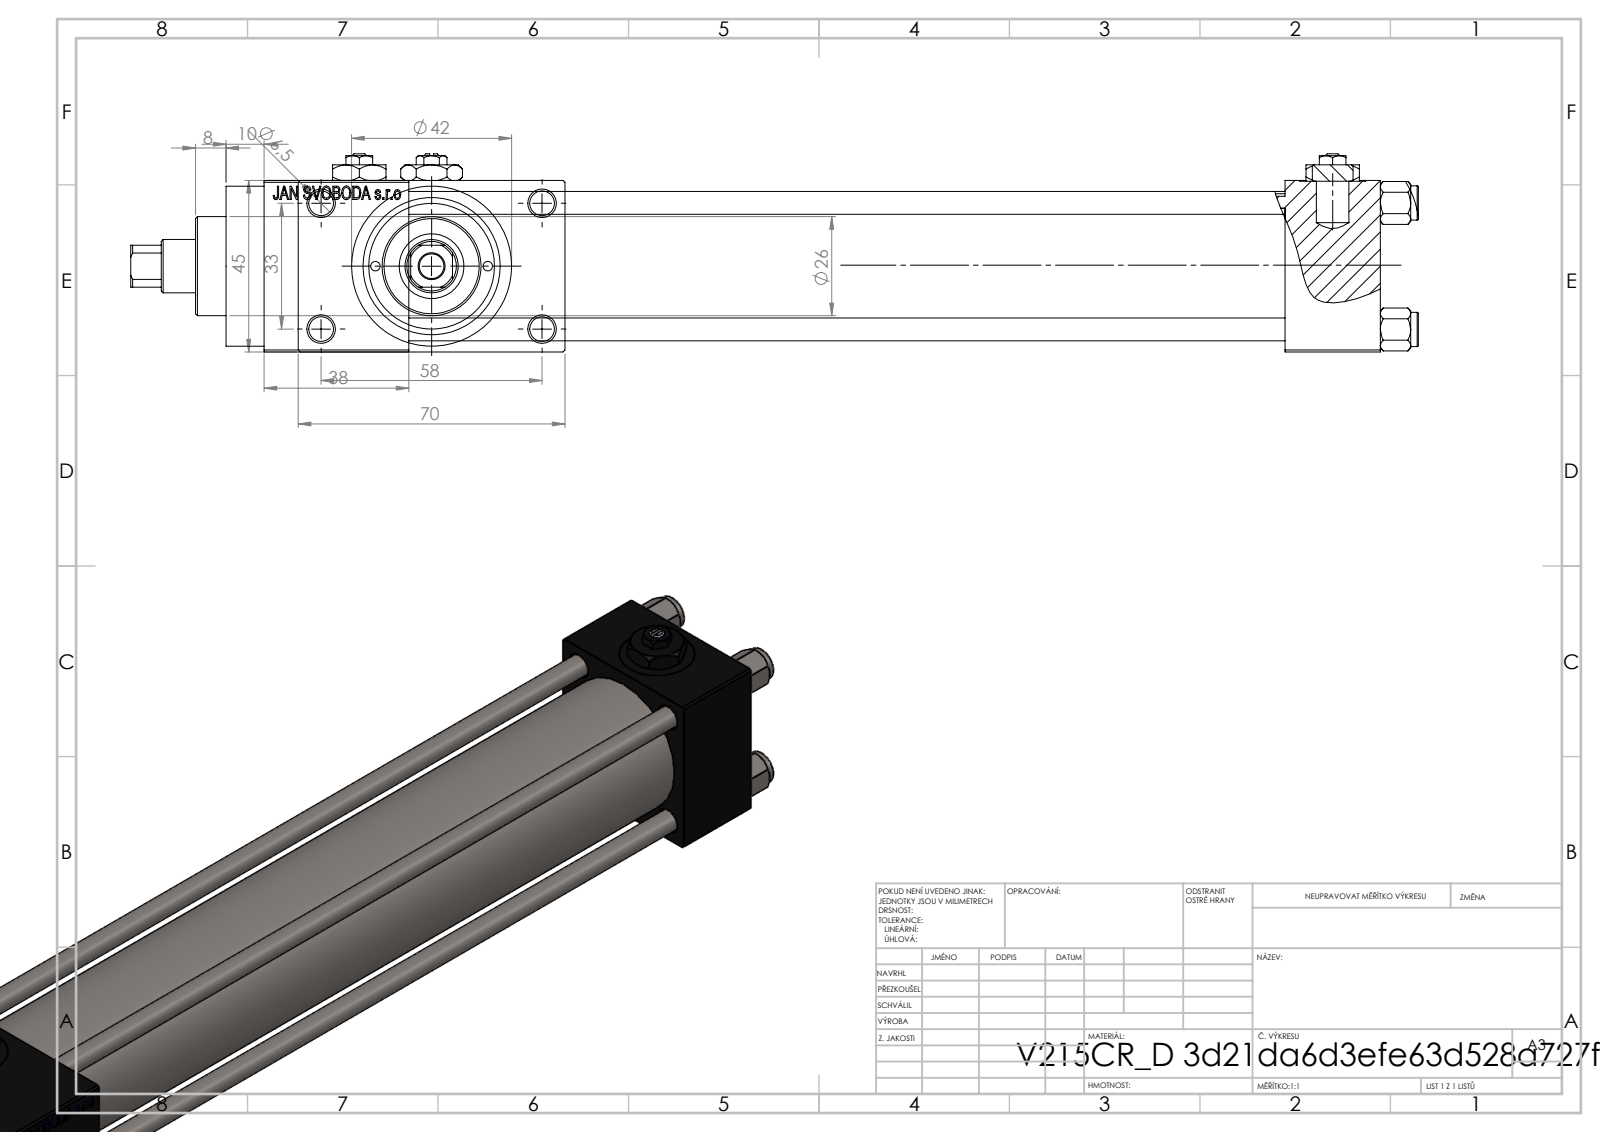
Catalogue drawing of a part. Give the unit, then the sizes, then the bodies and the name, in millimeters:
Units: millimetres
Overall size (bounding box): 338 × 70 × 52
Round holes (diameter × count): ⌀6.5 ×5, ⌀6 ×4, ⌀13.16 ×4, ⌀20 ×4, ⌀7 ×3, ⌀2.5 ×2, ⌀14 ×1, ⌀17 ×1, ⌀24 ×1, ⌀32 ×1, ⌀33 ×1
Round bosses / shafts (diameter × count): ⌀9 ×4, ⌀42 ×1, ⌀38 ×1, ⌀26 ×1
Partial cylindrical surfaces — rounded edges, fillets, slot ends (radius × count): R6.5 ×1
Main face-to-face distances: 45, 25, 12.5, 230, 255, 57.5, 268, 38, 293, 70
Hole centre spacings: 12.4, 16.7, 21.8, 23.48, 33.2, 33.37, 35.35, 35.47
Volume: 336 348 mm³ · Surface area: 138 191 mm²
Bodies: 13 solids, 1209 faces (544 planar, 103 cylindrical, 562 other)
Part name (STEP PRODUCT): NUT_M5_D; Zatka_pro_OIL_PORT; V215CR_D_Body; V215CR_D_TYCINKA (+2 more)
STEP written by: SolidWorks 2019 (CONFIG_CONTROL_DESIGN)
